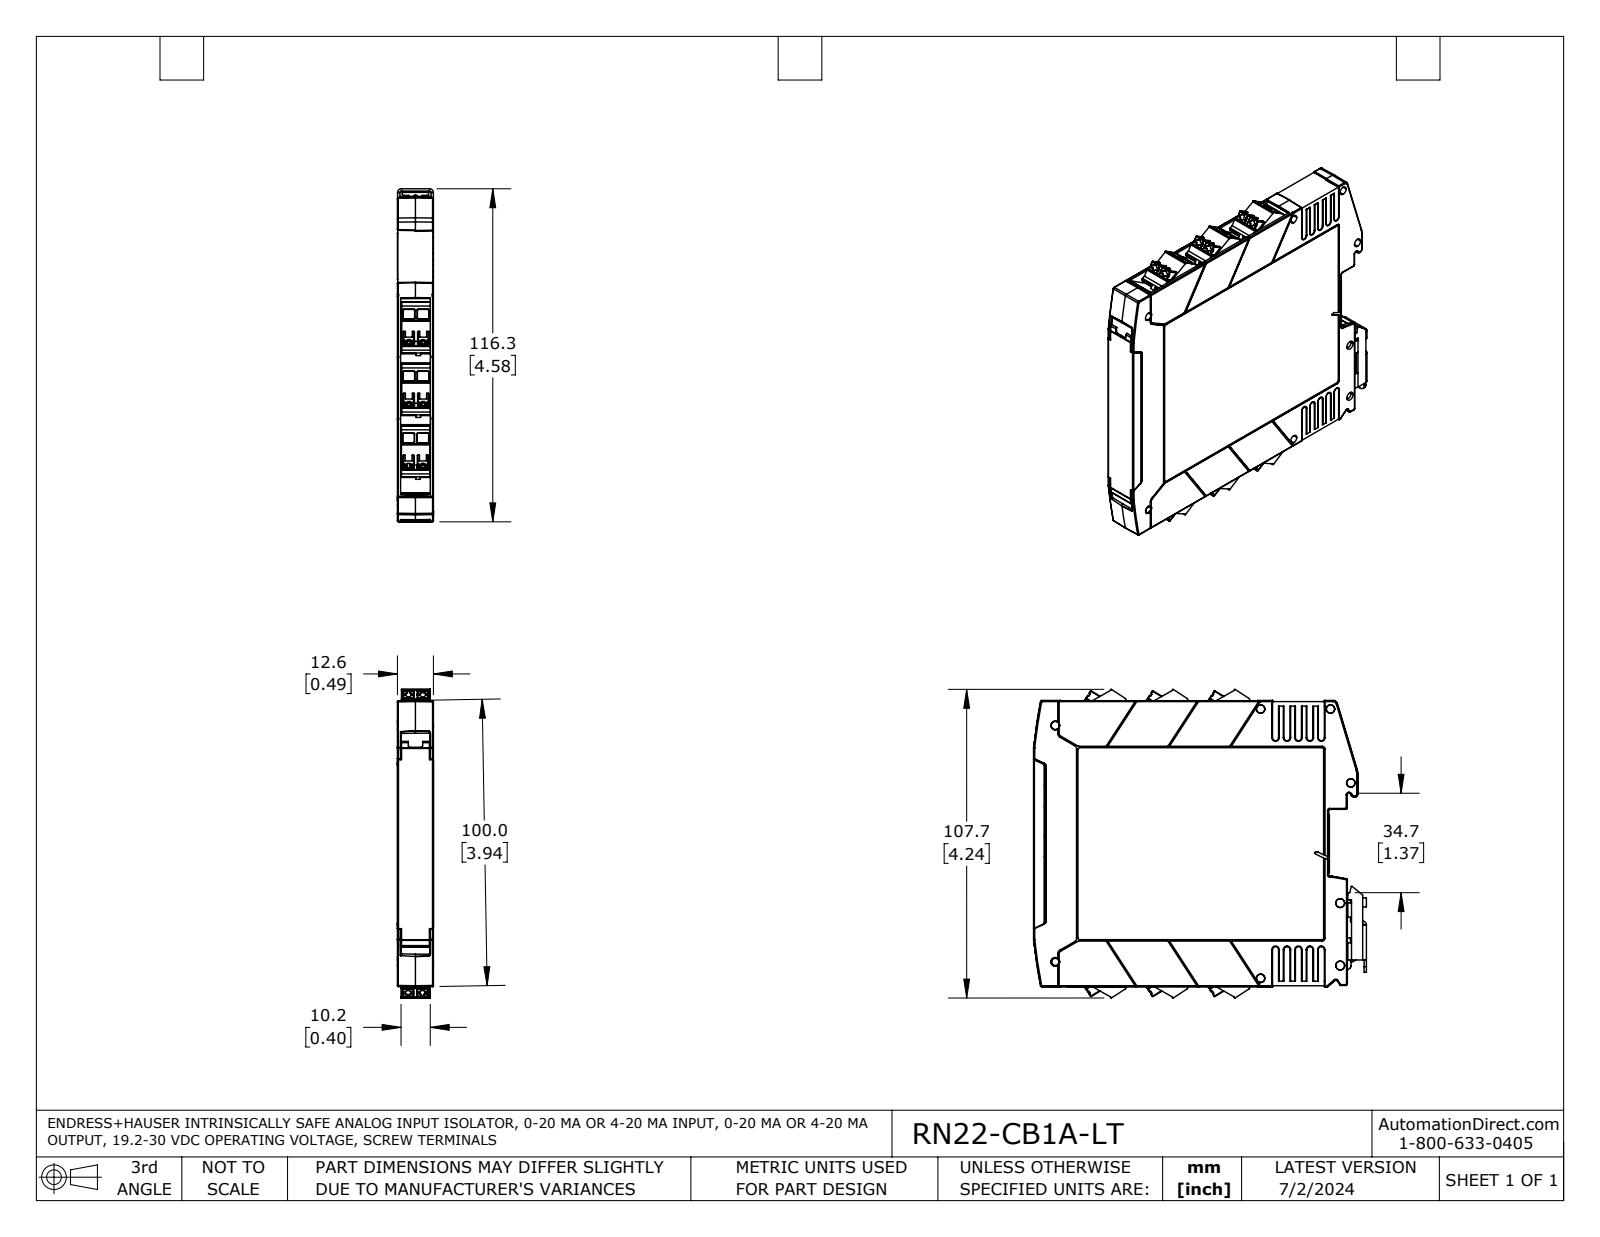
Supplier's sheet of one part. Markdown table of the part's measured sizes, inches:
| quantity | value |
| --- | --- |
| part name | RN22-CB1A-LT |
| STEP written by | SolidWorks 2021 (AUTOMOTIVE_DESIGN) |
| units | inches |
| bodies | 2 solids, 3045 faces (1939 planar, 765 cylindrical, 341 other) |
| overall size | 4.577 × 4.242 × 0.496 |
| volume | 8.127 in³ |
| surface area | 58.24 in² |
| round holes (diameter × count) | 0.118 × 3, 0.009 × 2, 0.097 × 1, 0.111 × 1 |
| partial cylindrical surfaces (radius × count) | 0.008 × 149, 0.02 × 71, 0.012 × 66, 0.039 × 28, 0.005 × 16, 0.114 × 12, 0.009 × 10, 0.024 × 10 |
| main face-to-face distances | 0.494, 0.043, 0.451, 0.039, 0.447, 0.047, 0.491, 0.435, 0.392, 0.031 |
| hole center spacings | 2.832, 4.477, 0.759, 0.76, 0.961, 2.073, 2.074, 3.031 |
